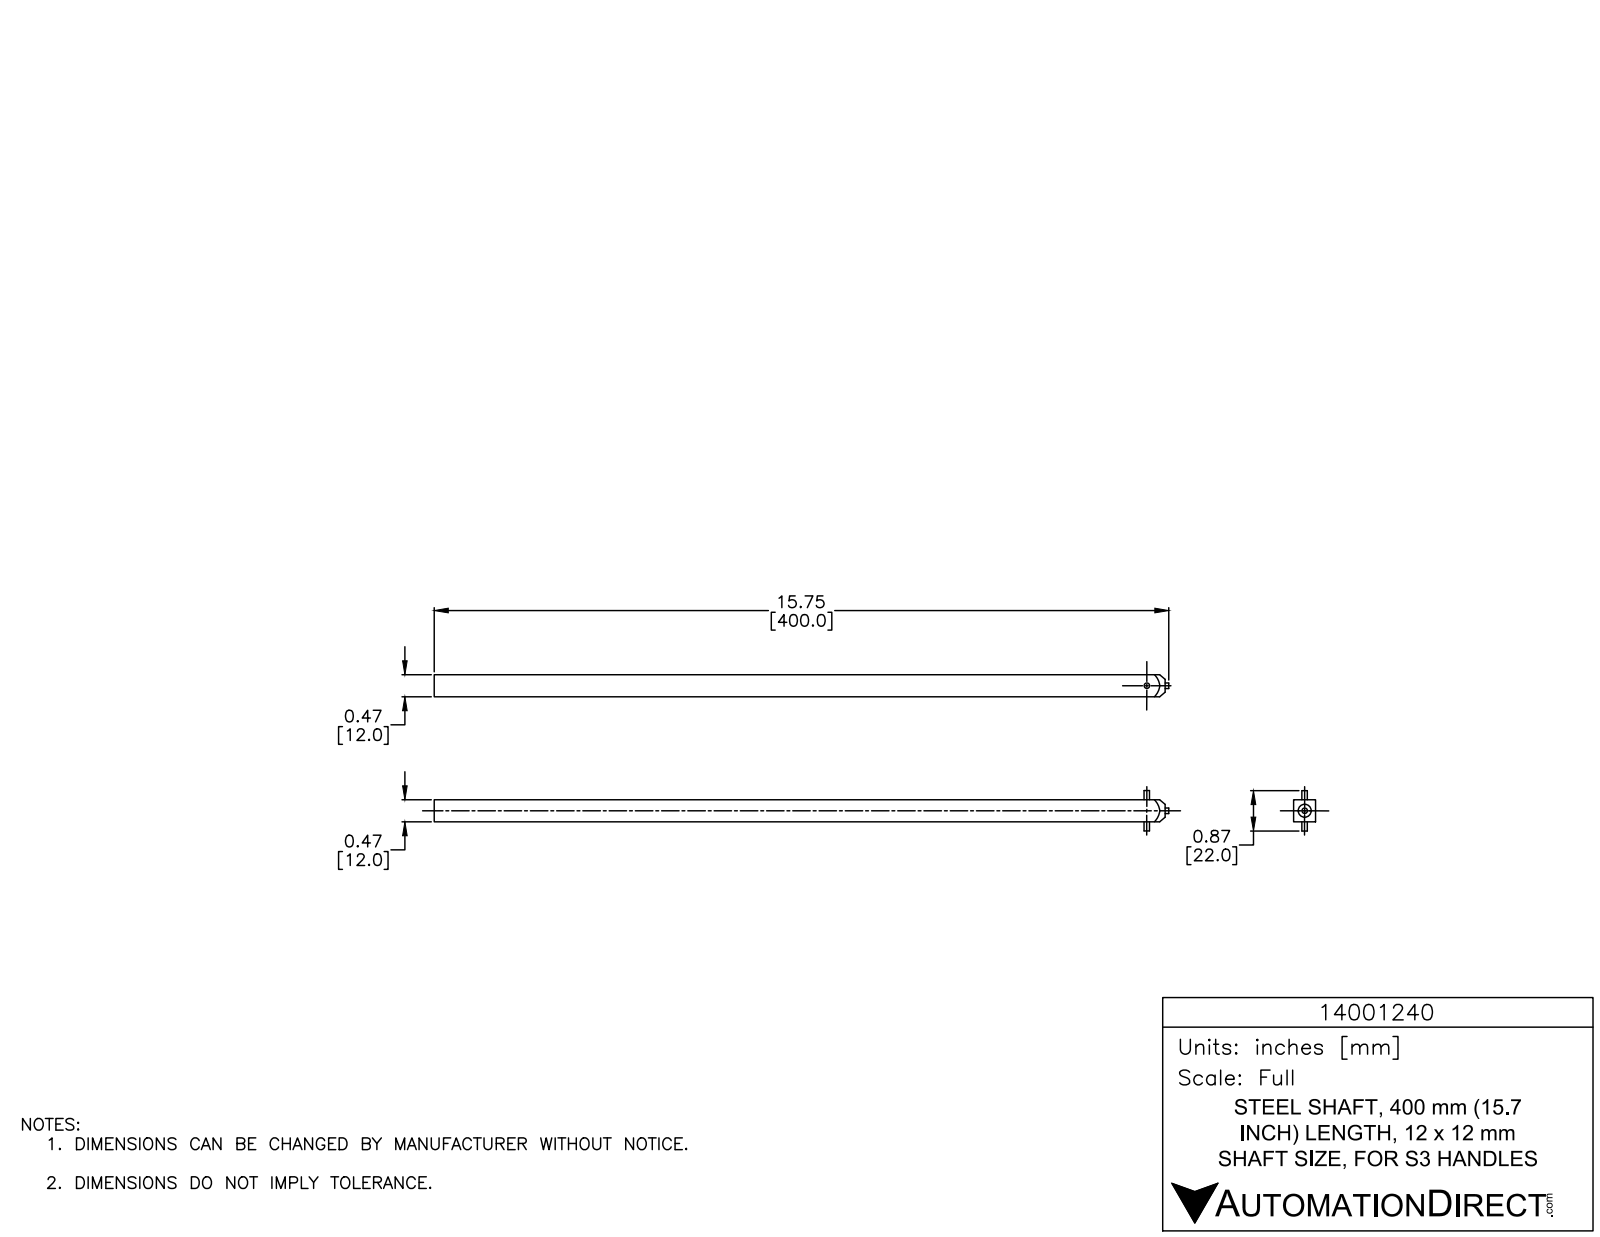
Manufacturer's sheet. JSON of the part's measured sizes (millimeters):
{"part_name": "14001240", "step_written_by": "SolidWorks 2015 (AUTOMOTIVE_DESIGN)", "units": "millimeters", "bodies": {"solids": 2, "faces": 19, "planar": 13, "cylindrical": 6, "other": 0}, "overall_size": [400, 22, 12], "volume_mm3": 57211, "surface_area_mm2": 19635, "round_holes": [[3.1, 1]], "round_bosses_or_shafts": [[3, 2]], "face_to_face_distances": [12, 398, 5, 17, 400, 2, 22]}
